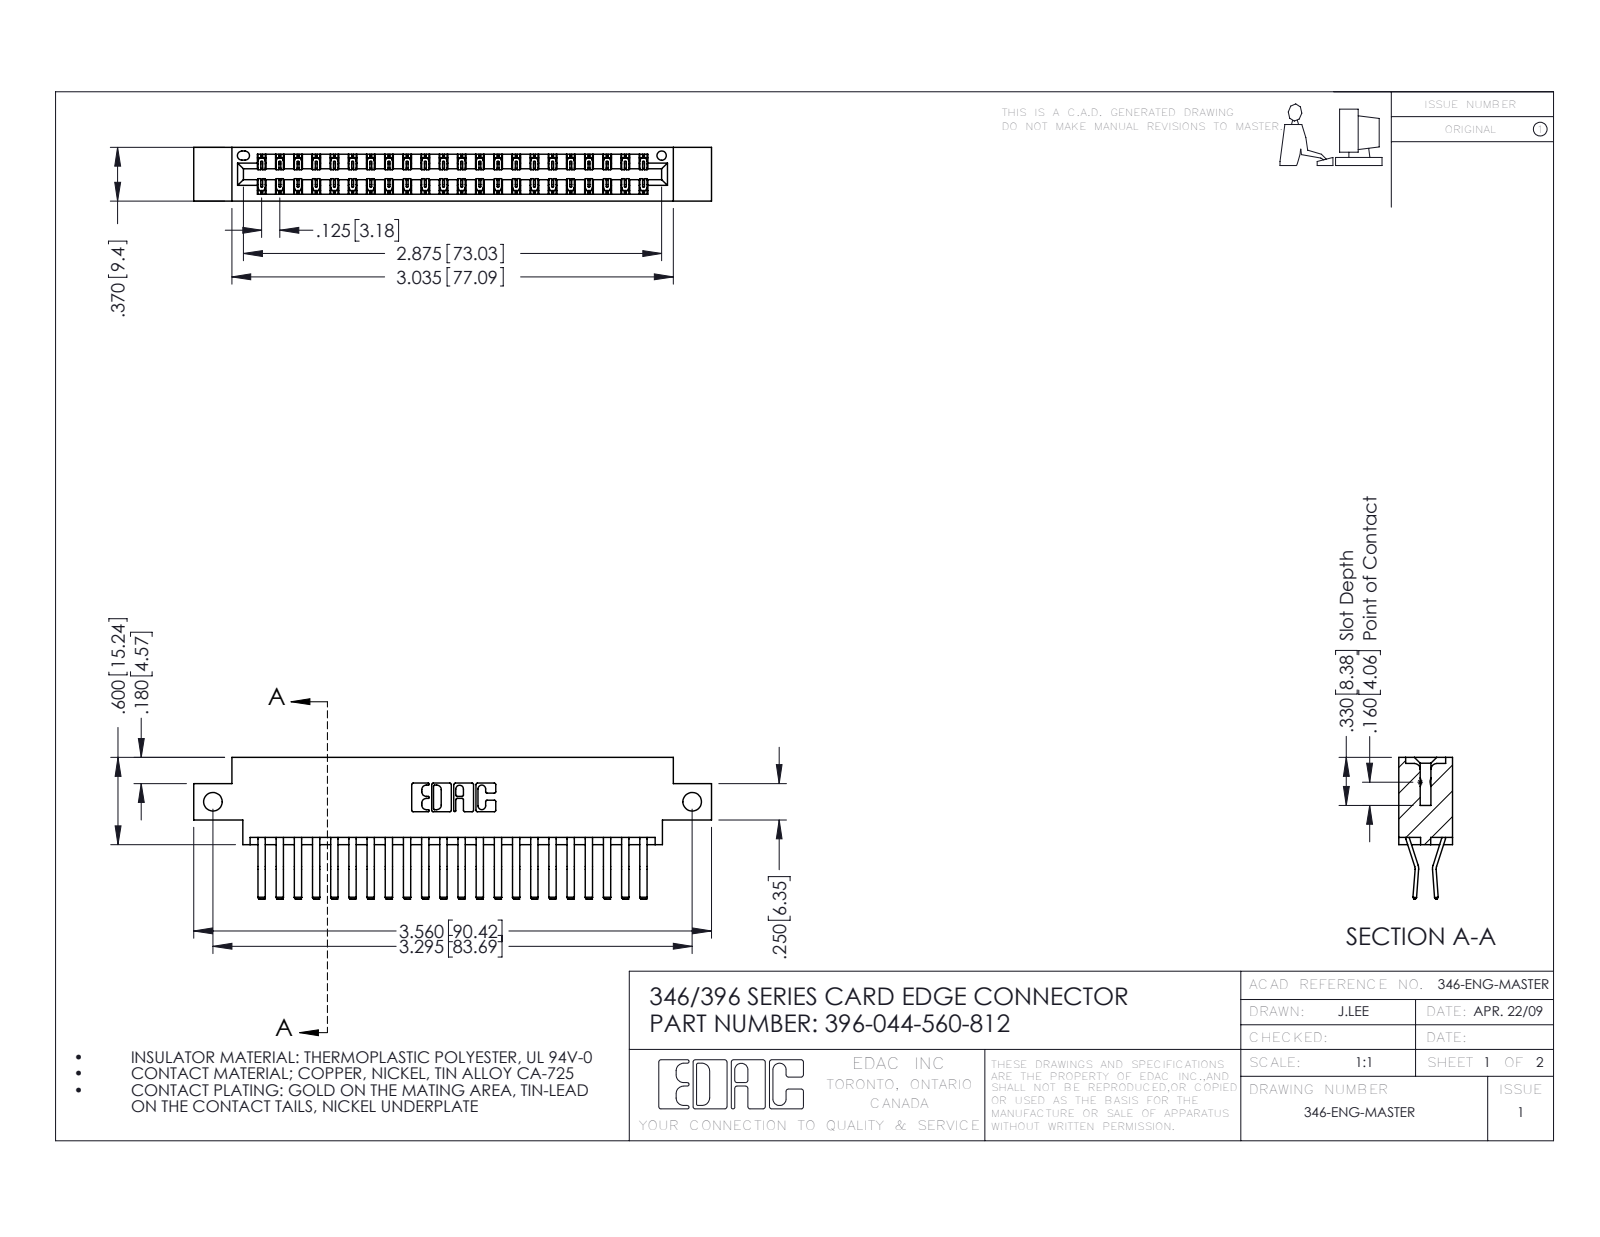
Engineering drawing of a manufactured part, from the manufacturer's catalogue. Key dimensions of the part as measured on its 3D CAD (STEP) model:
Part name (STEP PRODUCT): 396-044-560-812; 345-292-001_560 Tail; 346 Part_0.170 Offset - Side Mount
STEP written by: SolidWorks 2016 (CONFIG_CONTROL_DESIGN)
Units: inches
Bodies: 45 solids, 2502 faces (1620 planar, 882 cylindrical, 0 other)
Overall size (bounding box): 3.56 × 0.975 × 0.37
Volume: 0.531 in³ · Surface area: 19.33 in²
Round holes (diameter × count): ⌀0.128 ×2, ⌀0.064 ×1
Partial cylindrical surfaces — rounded edges, fillets, slot ends (radius × count): R0.006 ×66, R0.01 ×22, R0.007 ×6, R0.031 ×6, R0.026 ×3, R0.01 ×2, R0.014 ×2, R0.022 ×2
Main face-to-face distances: 0.048, 0.322, 0.37, 0.25, 0.025, 0.072, 0.298, 0.275, 0.148, 0.222
Hole centre spacings: 3.295
